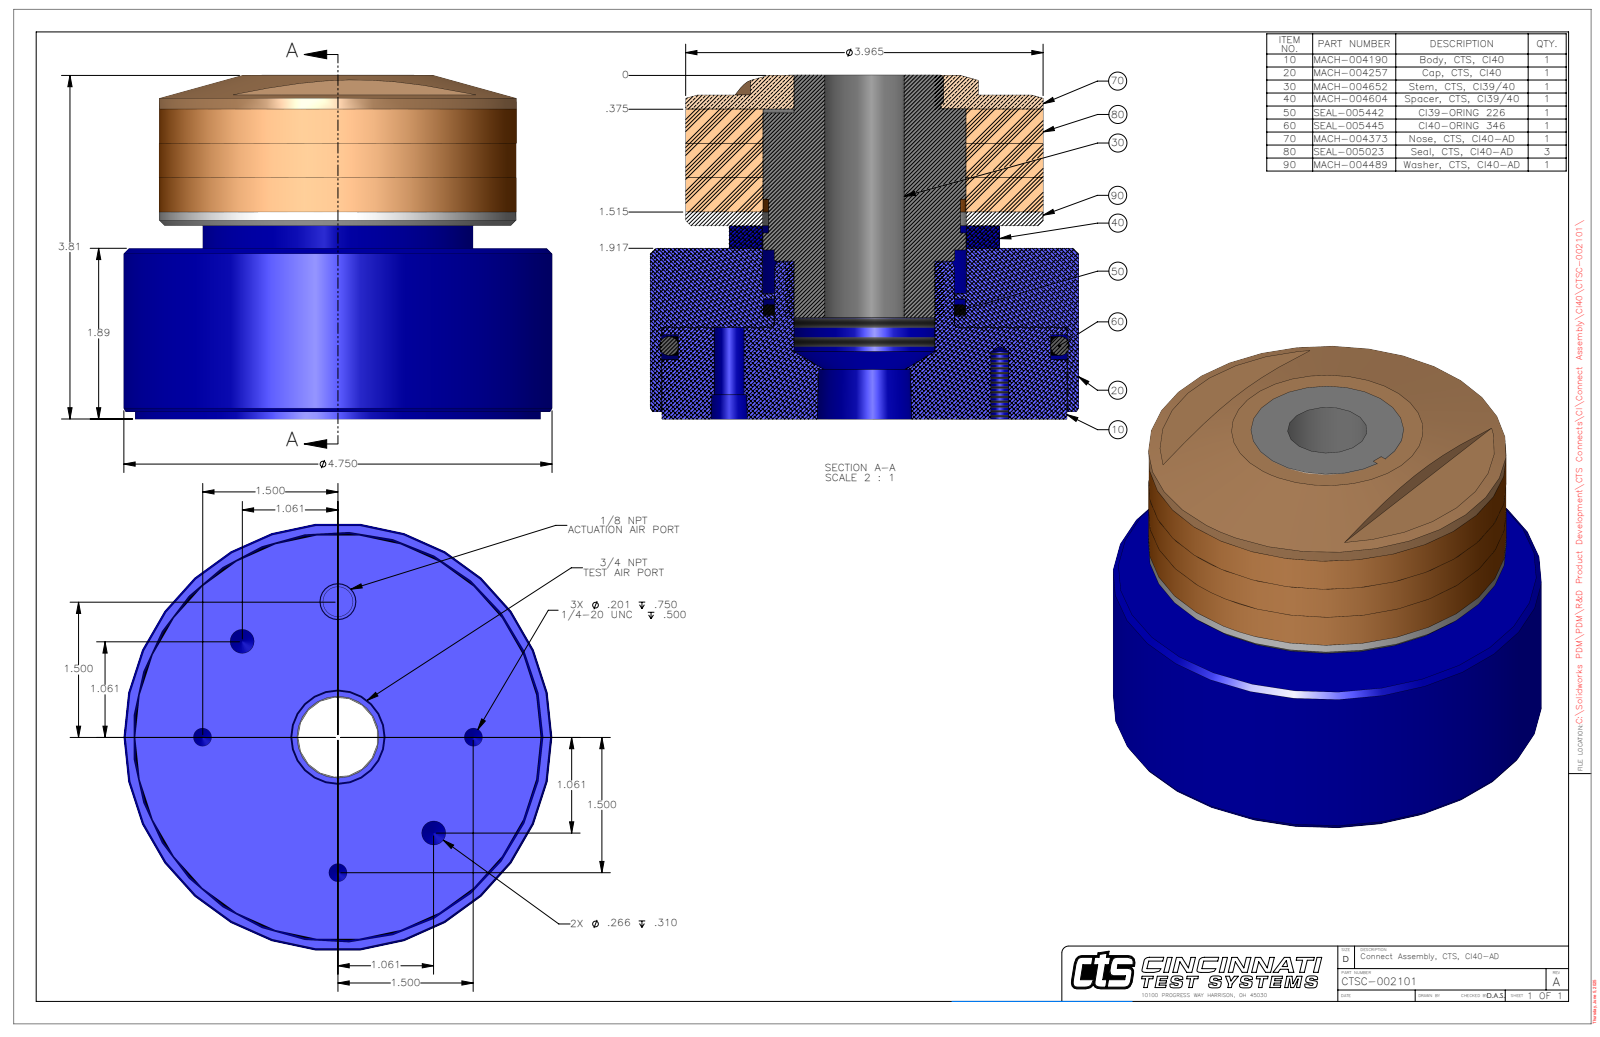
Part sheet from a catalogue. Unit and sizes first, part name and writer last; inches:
Units: inches
Overall size (bounding box): 4.75 × 4.75 × 3.813
Round holes (diameter × count): ⌀0.201 ×3, ⌀0.266 ×2, ⌀0.332 ×1, ⌀0.88 ×1, ⌀2.25 ×1, ⌀2.26 ×1, ⌀2.261 ×1, ⌀4.5 ×1
Round bosses / shafts (diameter × count): ⌀4.75 ×1, ⌀4.492 ×1, ⌀3.965 ×1, ⌀3 ×1, ⌀2.12 ×1
Partial cylindrical surfaces — rounded edges, fillets, slot ends (radius × count): R0.062 ×1, R0.781 ×1
Main face-to-face distances: 1.893, 2.143, 0.25, 3.591, 1.698, 1.448, 3.813, 1.92, 1.67, 0.222
Hole centre spacings: 1.5, 1.148, 2.121, 2.772, 3
Volume: 51.63 in³ · Surface area: 126.2 in²
Bodies: 1 solid, 94 faces (32 planar, 39 cylindrical, 23 other)
Part name (STEP PRODUCT): CTSC-002101
STEP written by: SolidWorks 2023 (AUTOMOTIVE_DESIGN)
